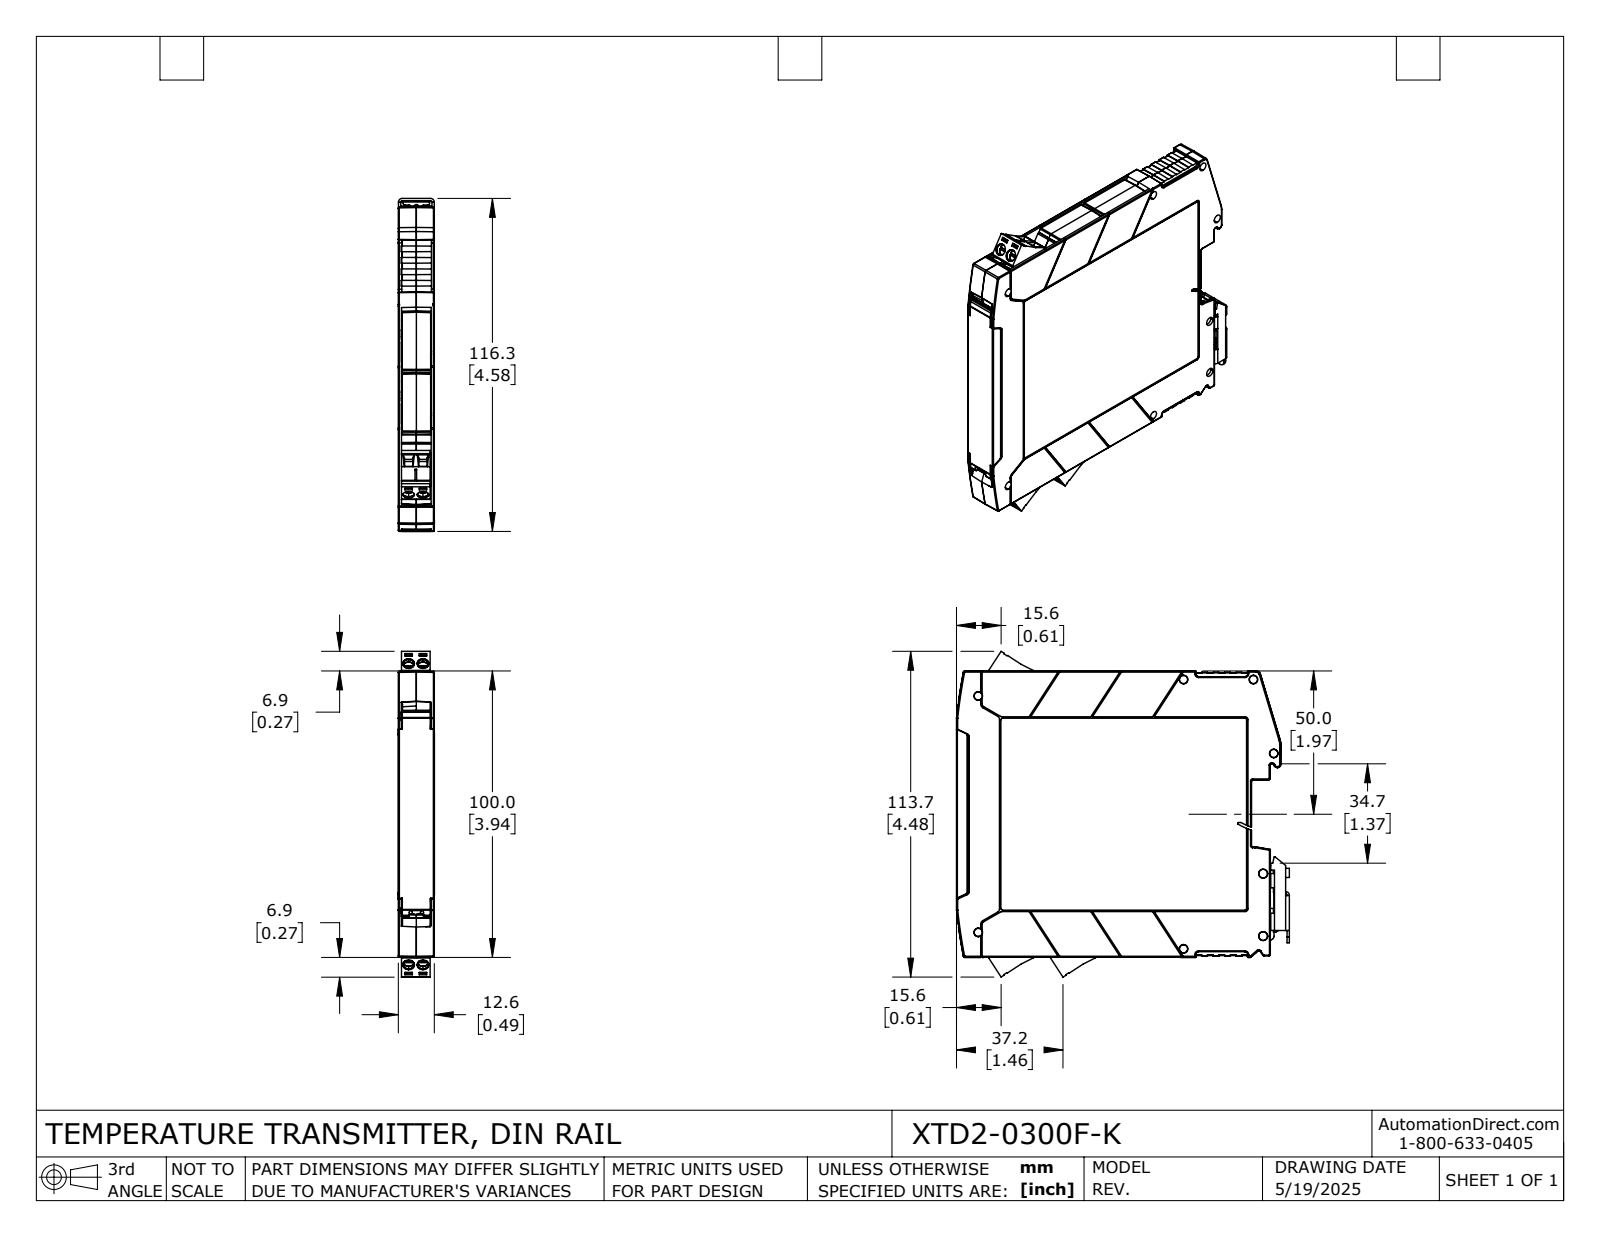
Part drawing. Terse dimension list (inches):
name: XTD2-0300F-K
written by: SolidWorks 2024 (AUTOMOTIVE_DESIGN)
unit: in
bodies: 14 solids, 3337 faces (1910 planar, 596 cylindrical, 831 other)
size: 4.577 × 4.478 × 0.496
volume: 2.41 in³; area: 101.5 in²
holes: 6× ⌀0.063, 6× ⌀0.11, 6× ⌀0.152, 6× ⌀0.159
bosses: 6× ⌀0.156, 6× ⌀0.098, 2× ⌀0.059, 2× ⌀0.053
rounds: 89× R0.008, 78× R0.012, 71× R0.02, 22× R0.039, 20× R0.004, 13× R0.016, 12× R0.006, 8× R0.028
face distances: 0.049, 0.445, 0.494, 0.396, 0.043, 0.451, 0.402, 0.031, 0.198, 0.247
hole spacings: 0.197, 0.464, 0.504, 0.713, 0.739
